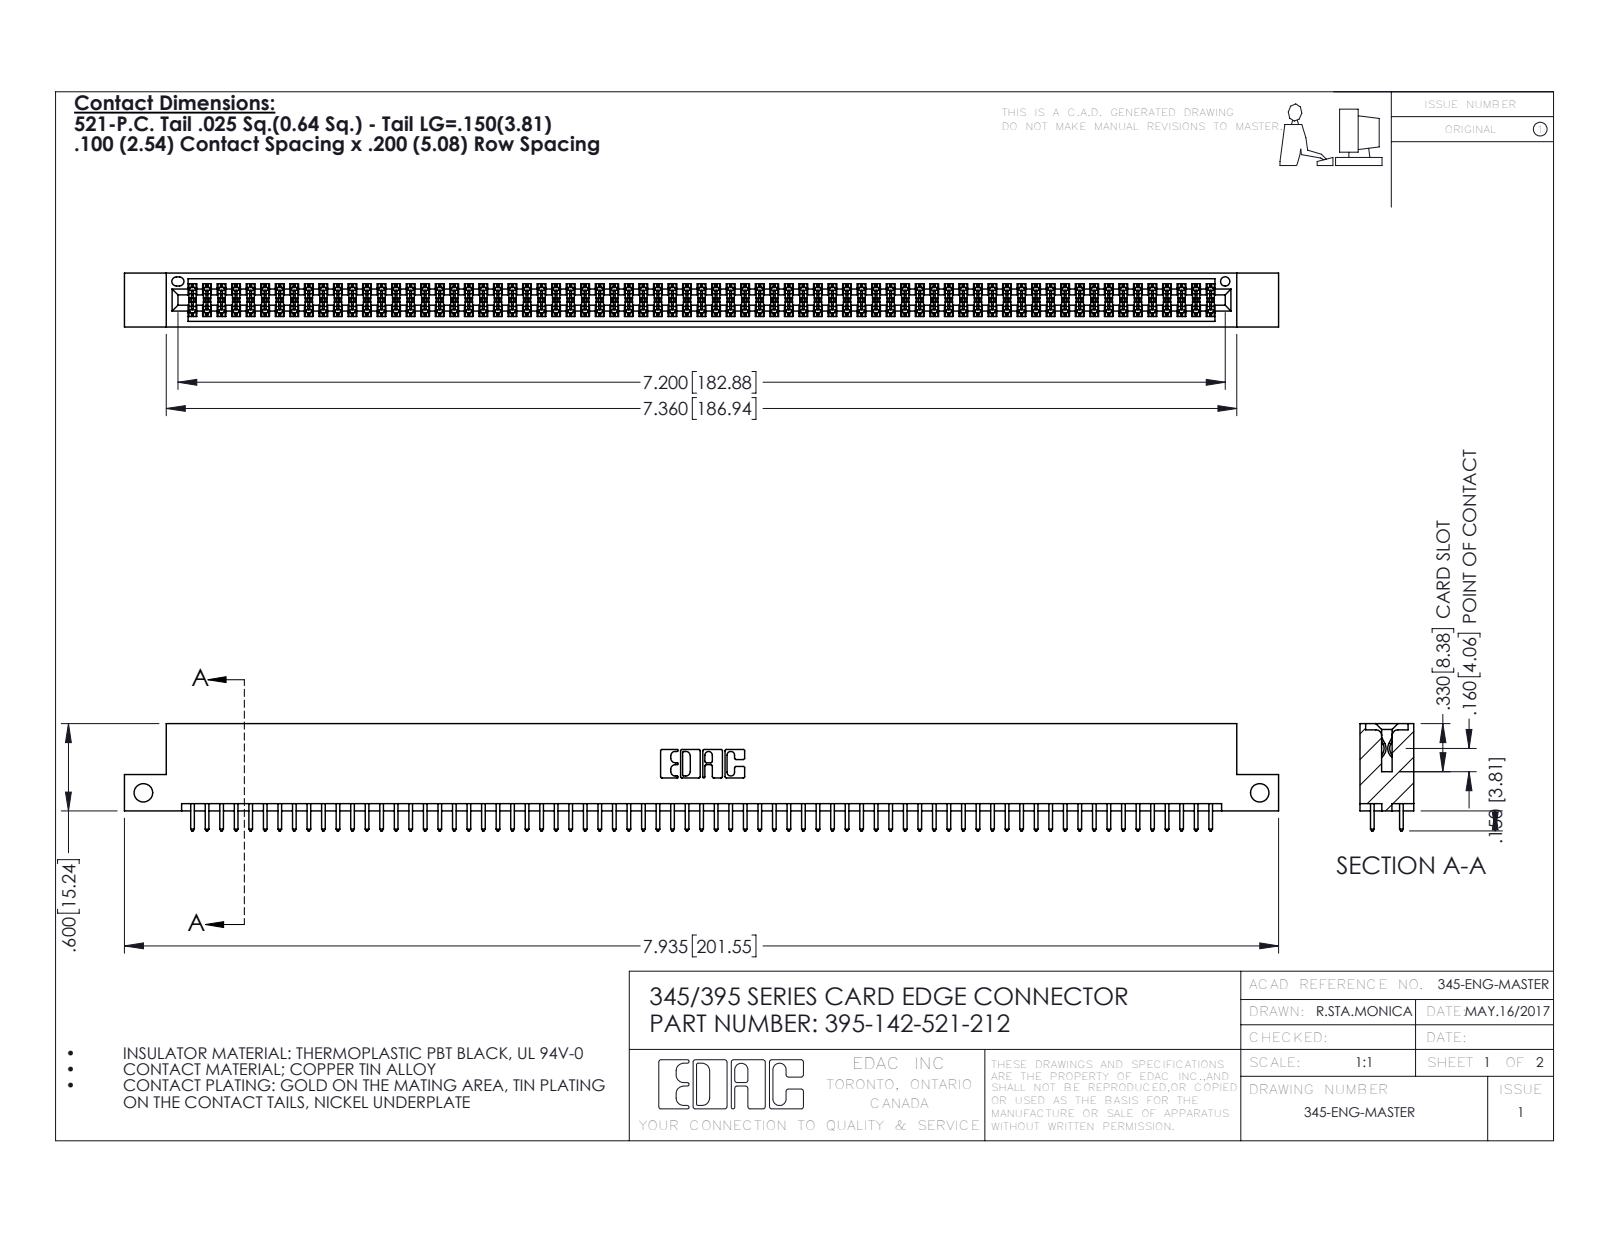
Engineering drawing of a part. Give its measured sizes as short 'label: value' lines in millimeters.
name: 345 Part_Flush Mounting Lugs - Side Mount; 345-292-001_345-293-121; 395-142-521-212
written by: SolidWorks 2016 (CONFIG_CONTROL_DESIGN)
unit: mm
bodies: 143 solids, 7226 faces (4766 planar, 2460 cylindrical, 0 other)
size: 201.5 × 18.7 × 9.4
volume: 19 700 mm³; area: 29 170 mm²
holes: 2× ⌀3.3, 1× ⌀1.6
rounds: 213× R0.2, 142× R0.3, 22× R0.3, 6× R0.2, 6× R0.8, 3× R0.7, 2× R0.4, 2× R0.5
face distances: 7.6, 1.8, 5.1, 2.5, 6.9, 0.6, 9.4, 5.7, 4.4, 3.8
hole spacings: 194.9
